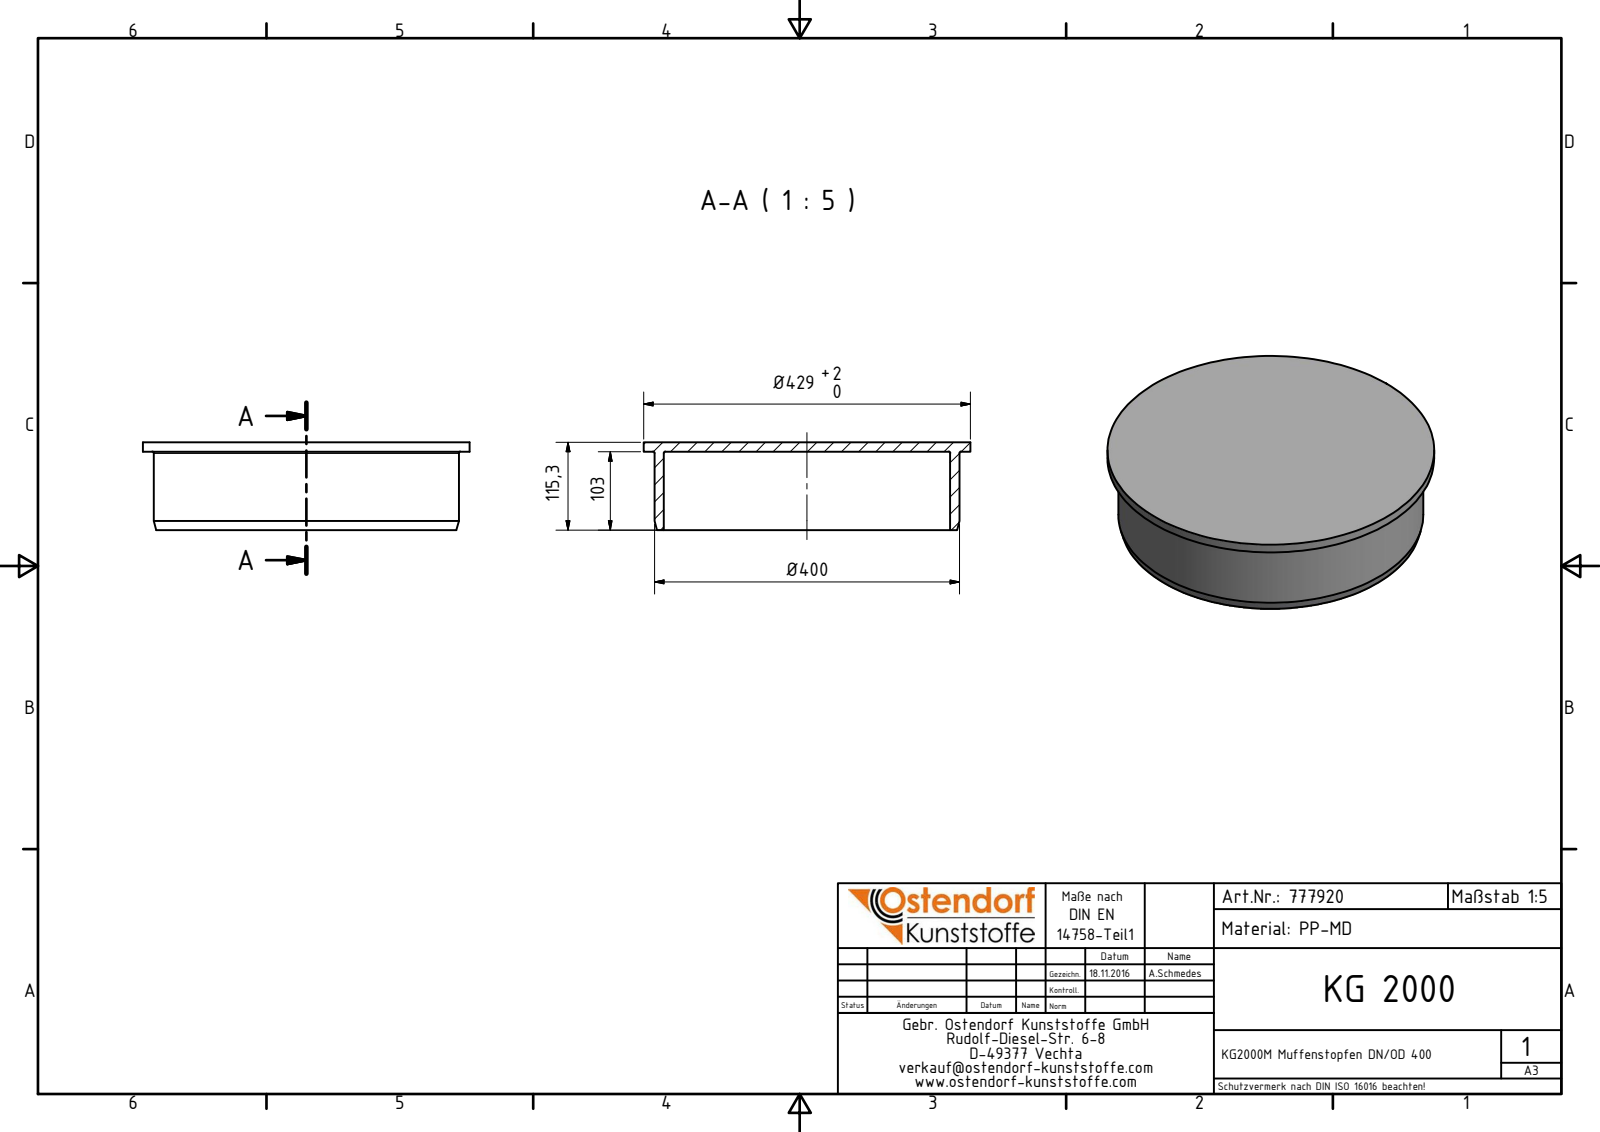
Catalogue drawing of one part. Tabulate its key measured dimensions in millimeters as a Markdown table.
| quantity | value |
| --- | --- |
| part name | 777920 KG2000M Muffenstopfen DN_OD 400 |
| STEP written by | Autodesk Inventor 2016 (AUTOMOTIVE_DESIGN) |
| units | millimeters |
| bodies | 1 solid, 10 faces (4 planar, 3 cylindrical, 3 other) |
| overall size | 429 × 429 × 115.3 |
| volume | 3 301 000 mm³ |
| surface area | 551 199 mm² |
| round holes (diameter × count) | 375.9 × 1 |
| round bosses / shafts (diameter × count) | 429 × 1, 400.5 × 1 |
| main face-to-face distances | 12.3, 103, 115.3 |
